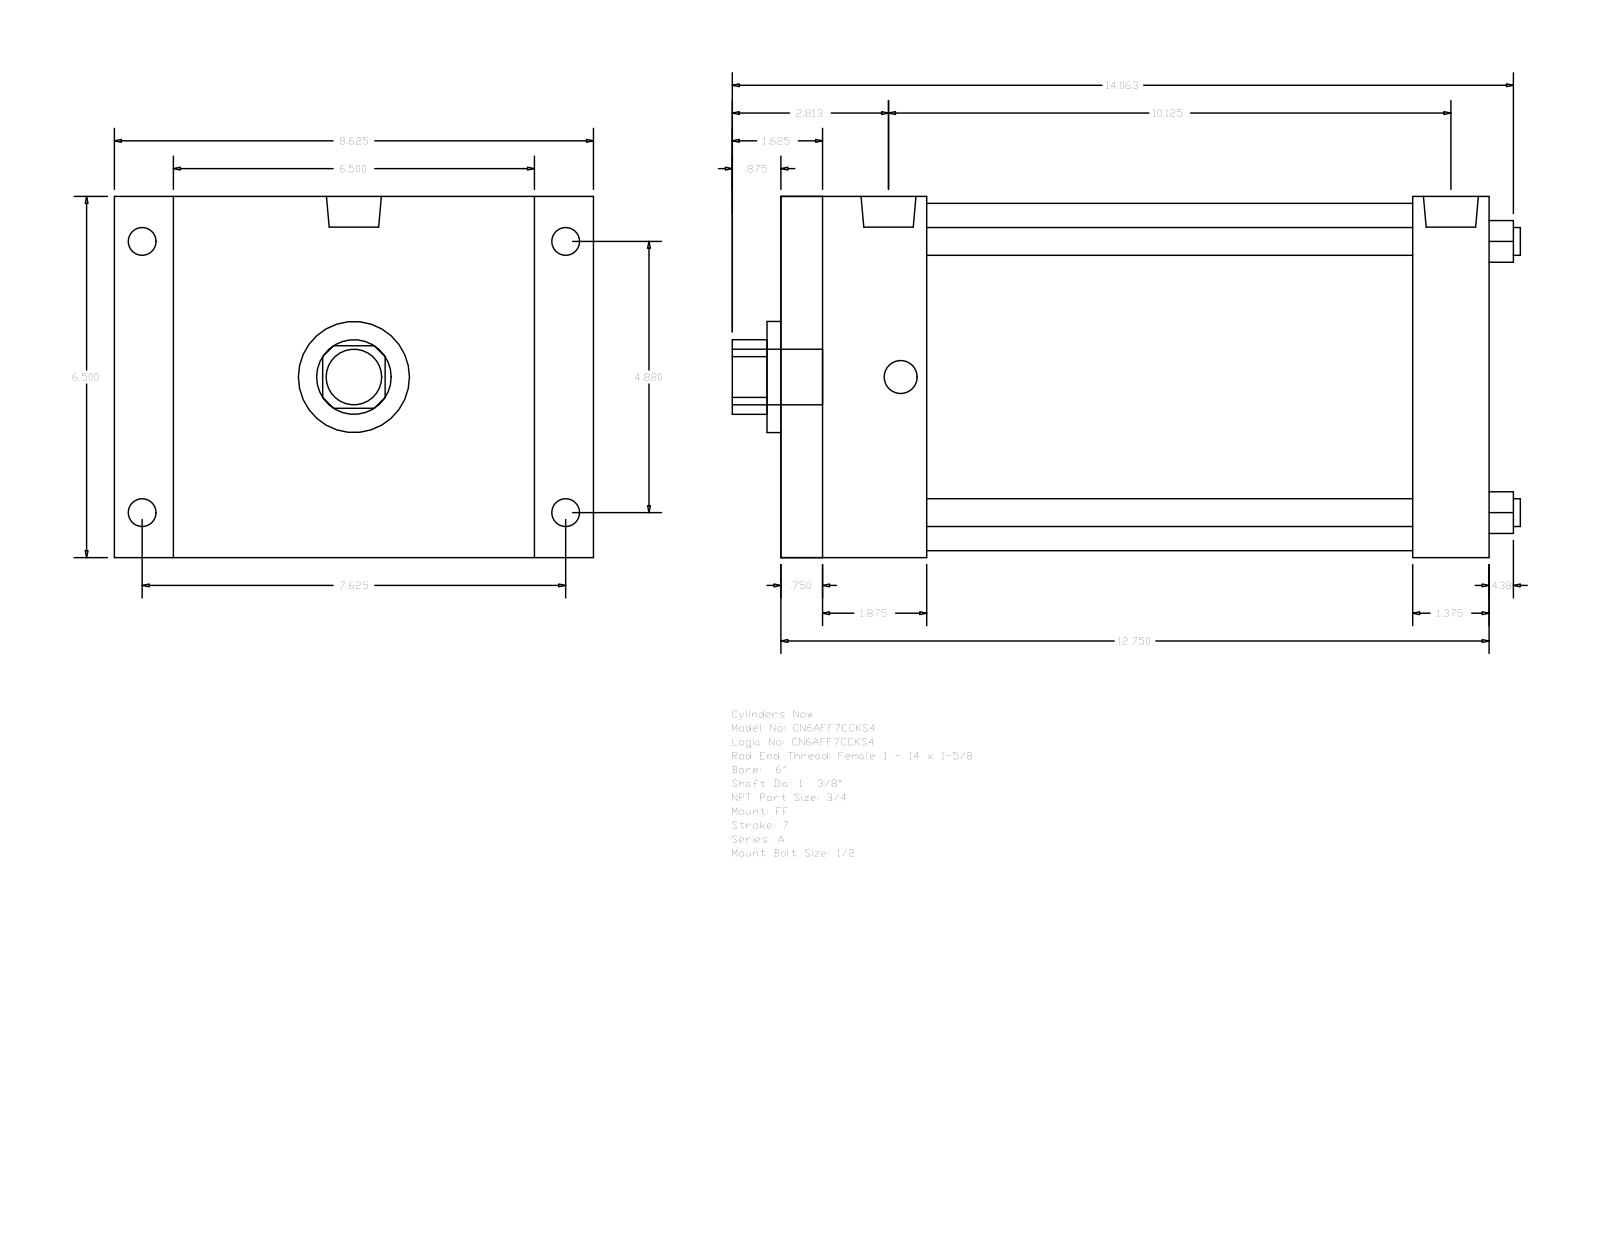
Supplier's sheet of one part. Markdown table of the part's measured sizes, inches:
| quantity | value |
| --- | --- |
| part name | A_FF__0600_1.375 |
| STEP written by | GSSL Pune (CONFIG_CONTROL_DESIGN) |
| units | inches |
| bodies | 0 solids, 92 faces (64 planar, 28 cylindrical, 0 other) |
| overall size | 14.187 × 8.625 × 6.5 |
| round holes (diameter × count) | 0.5 × 4, 1.375 × 1, 2 × 1, 6.25 × 1 |
| round bosses / shafts (diameter × count) | 0.594 × 4, 0.5 × 4, 0.989 × 2, 1 × 1 |
| partial cylindrical surfaces (radius × count) | 0.672 × 1 |
| main face-to-face distances | 6.5, 12.75, 0.75, 12, 2.625, 1.875, 10.125, 11.375, 10.625, 8.75 |
| hole center spacings | 3.451, 4.88, 6.902 |
